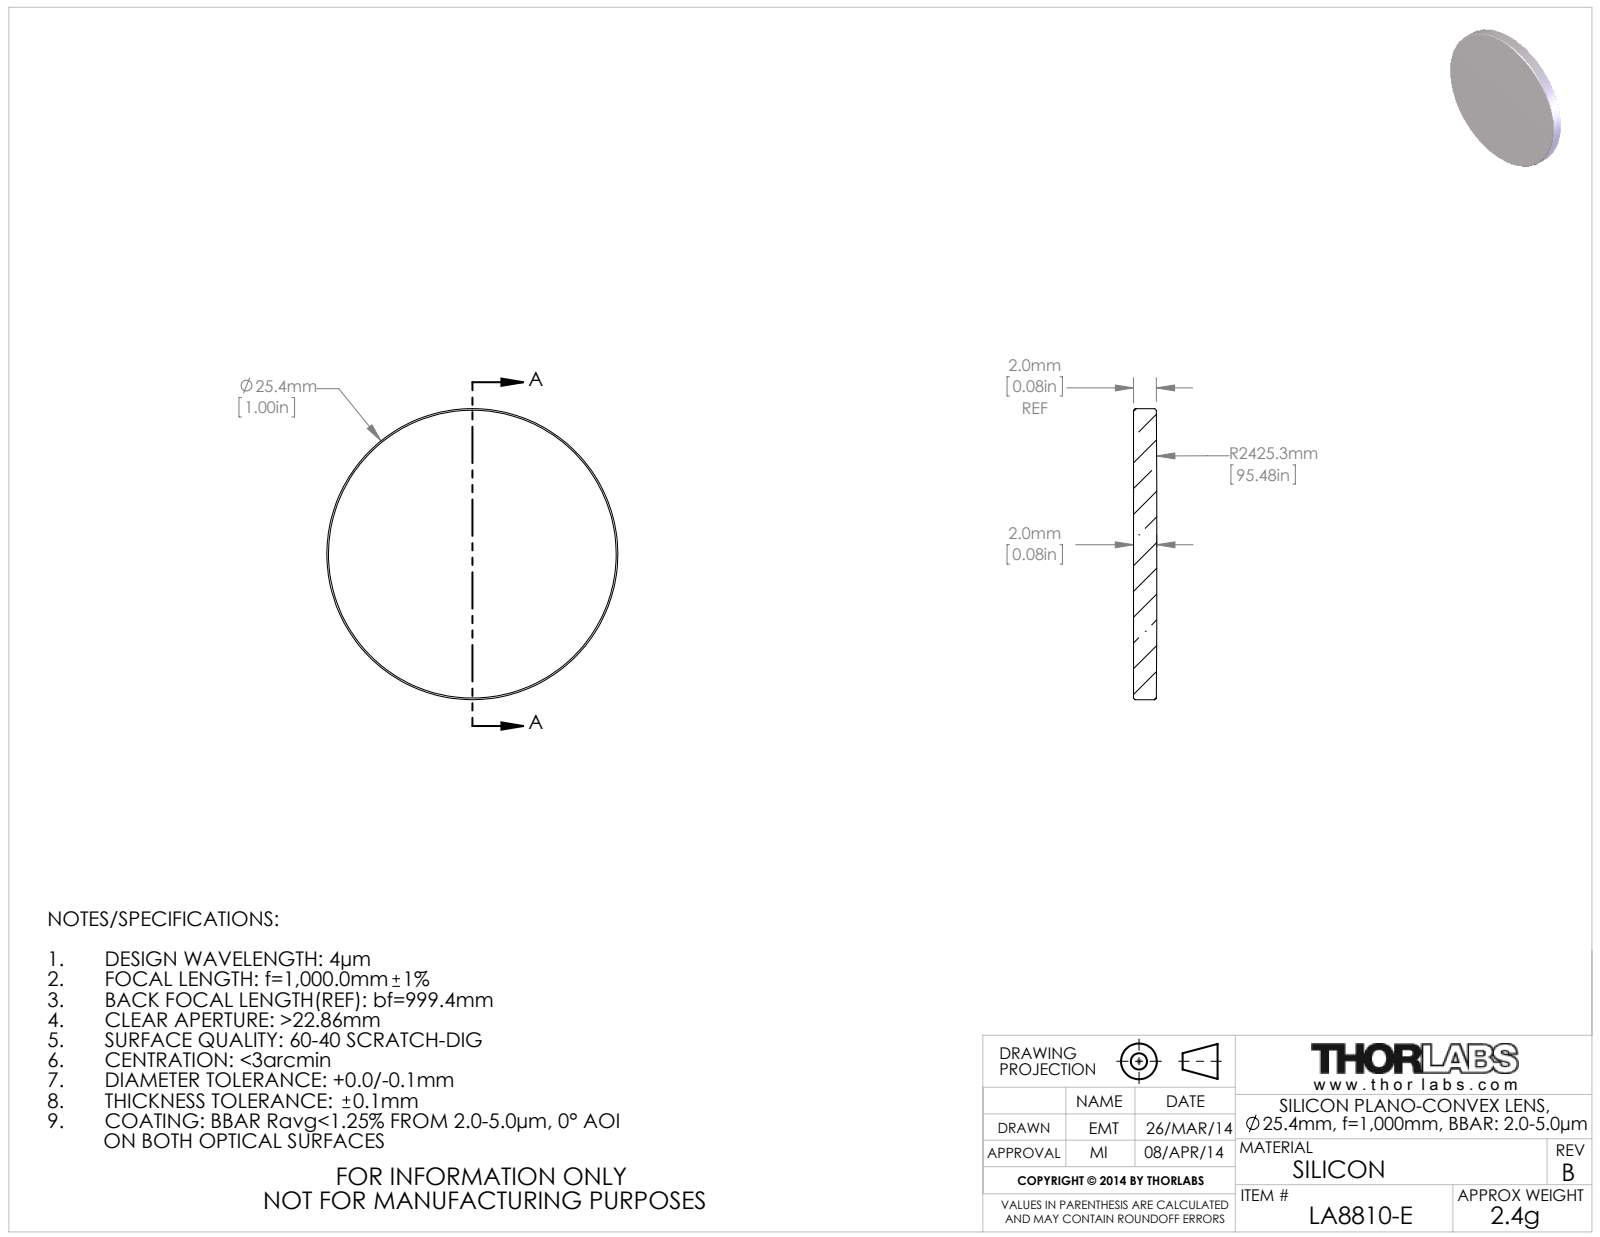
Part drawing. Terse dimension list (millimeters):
name: 20124-E0W
written by: SolidWorks 2014 (CONFIG_CONTROL_DESIGN)
unit: mm
bodies: 1 solid, 9 faces (1 planar, 2 cylindrical, 6 other)
size: 25.4 × 25.4 × 2.03
volume: 1 019 mm³; area: 1 160 mm²
bosses: 1× ⌀25.4
